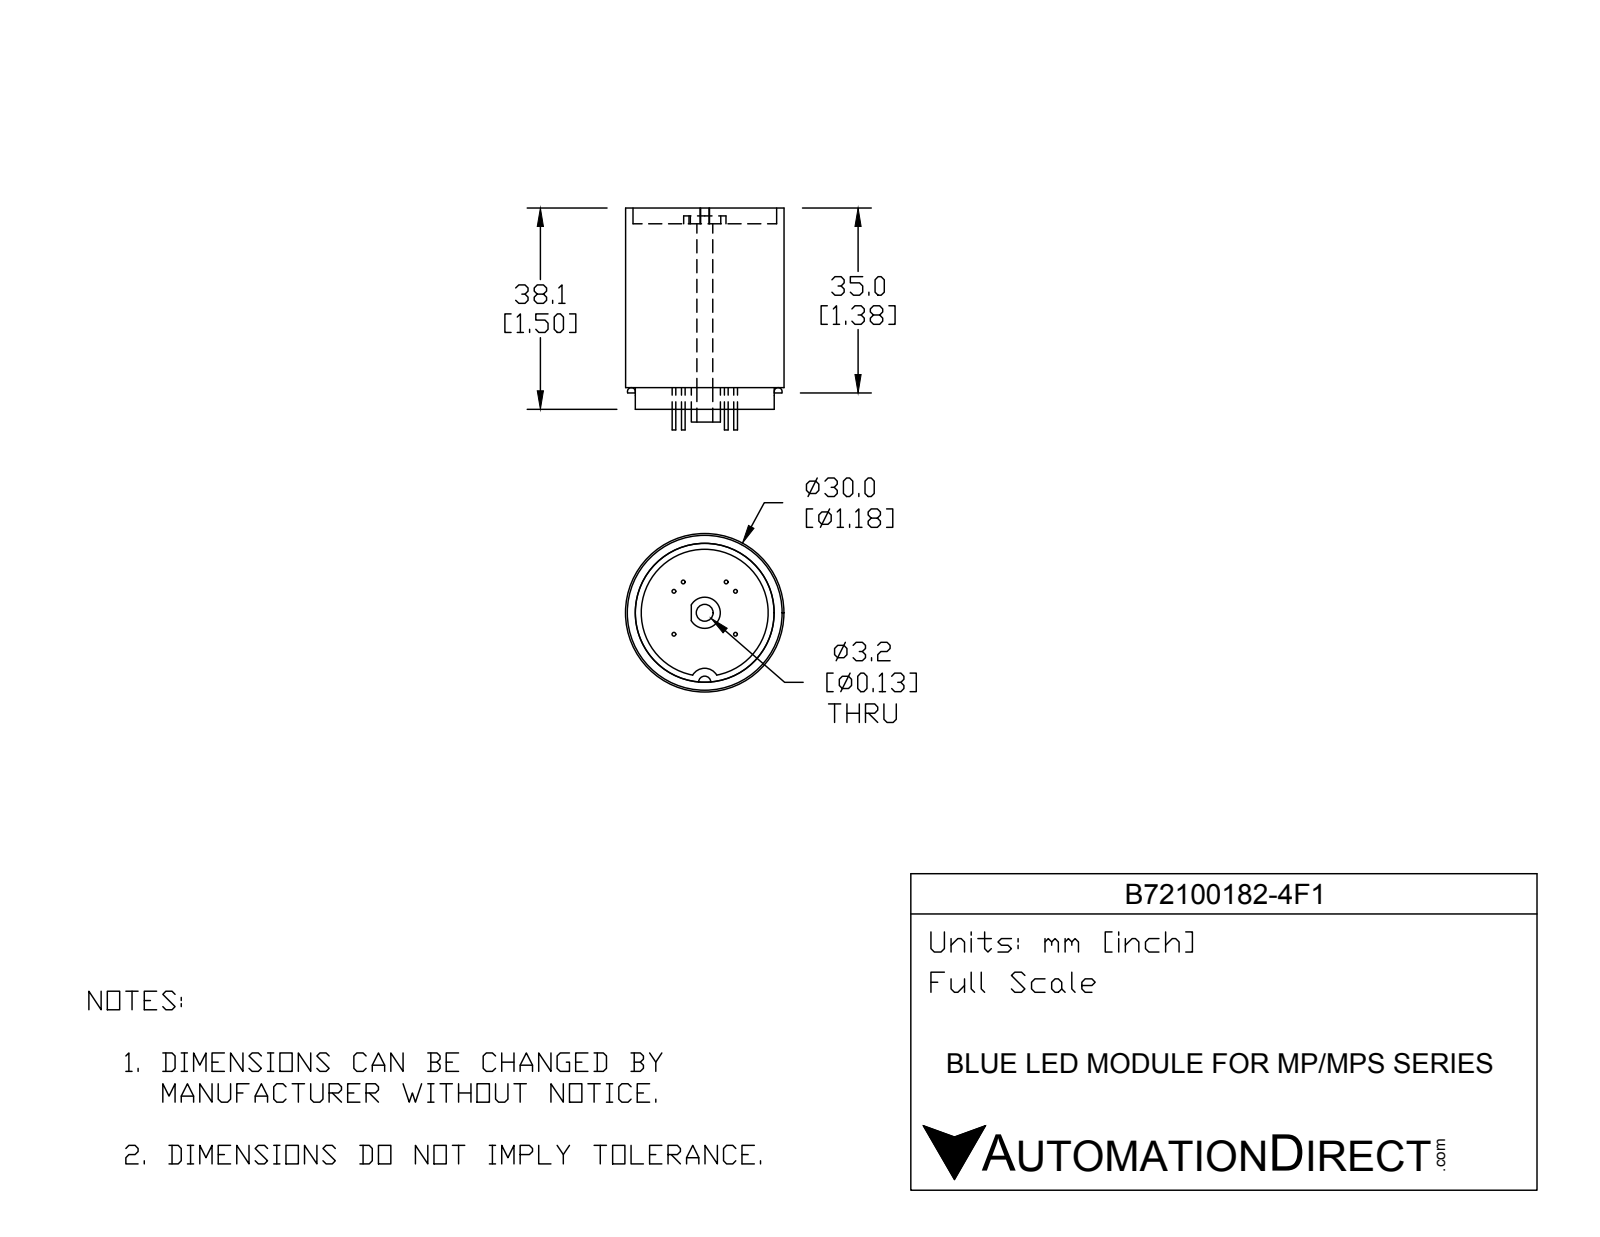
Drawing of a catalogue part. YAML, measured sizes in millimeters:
part_name: "B72100182-4F1"
step_written_by: "SolidWorks 2016 (AUTOMOTIVE_DESIGN)"
units: millimeters
bodies: {solids: 10, faces: 64, planar: 25, cylindrical: 35, other: 4}
overall_size: [42, 30, 30]
volume: 22787
surface_area: 6668
round_holes:
  - {diameter: 3, count: 1}
  - {diameter: 6.06, count: 1}
  - {diameter: 24.04, count: 1}
  - {diameter: 27.2, count: 1}
round_bosses_or_shafts:
  - {diameter: 0.7, count: 6}
  - {diameter: 30, count: 1}
  - {diameter: 26.3, count: 1}
  - {diameter: 8, count: 1}
  - {diameter: 5.9, count: 1}
partial_cylinders:
  - {radius: 0.9, count: 1}
  - {radius: 1.15, count: 1}
  - {radius: 2.65, count: 1}
face_to_face_distances: [31, 34, 3, 4.1, 35.1, 38.1, 1.5, 36.6, 32.5, 2.42]
